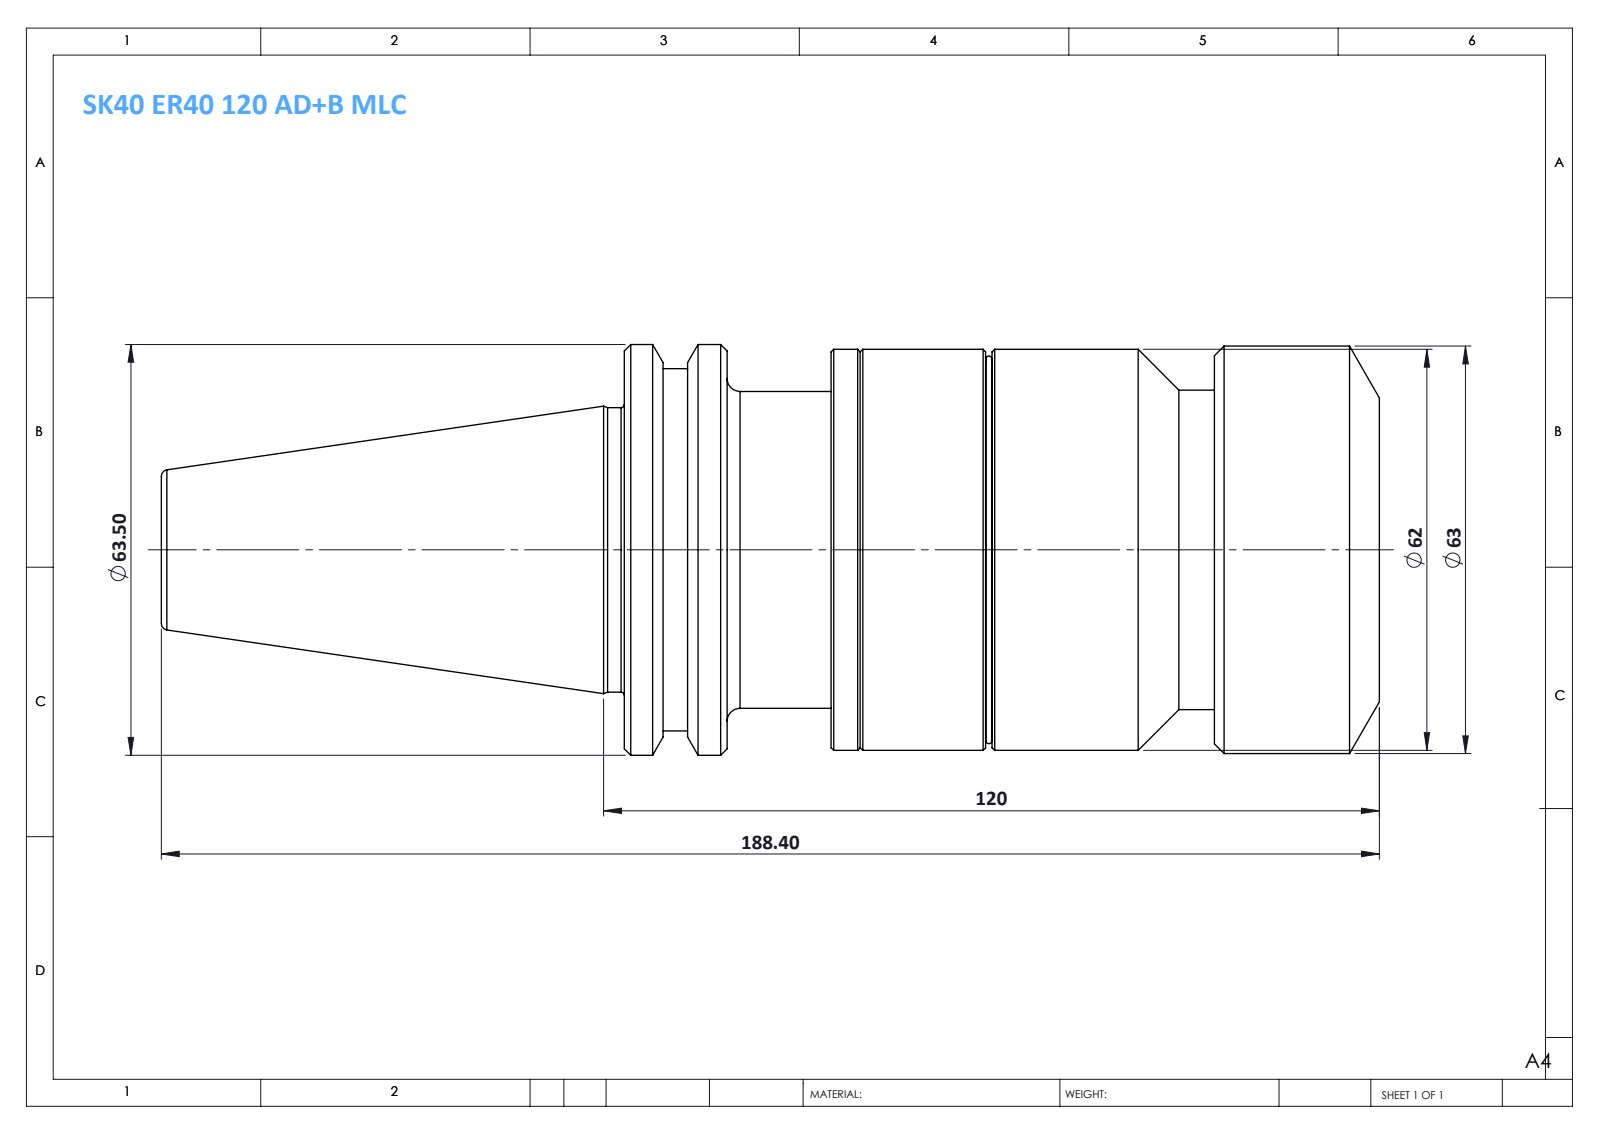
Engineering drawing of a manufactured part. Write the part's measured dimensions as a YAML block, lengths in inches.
part_name: "SK 40 ER 40 120 AD+B MLC"
step_written_by: "SolidWorks 2014 (CONFIG_CONTROL_DESIGN)"
units: inches
bodies: {solids: 2, faces: 70, planar: 10, cylindrical: 22, other: 38}
overall_size: [7.417, 2.5, 2.5]
volume: 23.95
surface_area: 61.8
round_bosses_or_shafts:
  - {diameter: 2.5, count: 1}
  - {diameter: 2.48, count: 1}
  - {diameter: 2.441, count: 1}
  - {diameter: 2.283, count: 1}
  - {diameter: 2.205, count: 1}
  - {diameter: 1.945, count: 1}
  - {diameter: 1.929, count: 1}
  - {diameter: 1.732, count: 1}
face_to_face_distances: [4.598, 3.339, 1.26, 1.004, 2.335, 3.594, 3.972, 2.969, 0.634, 0.626]
